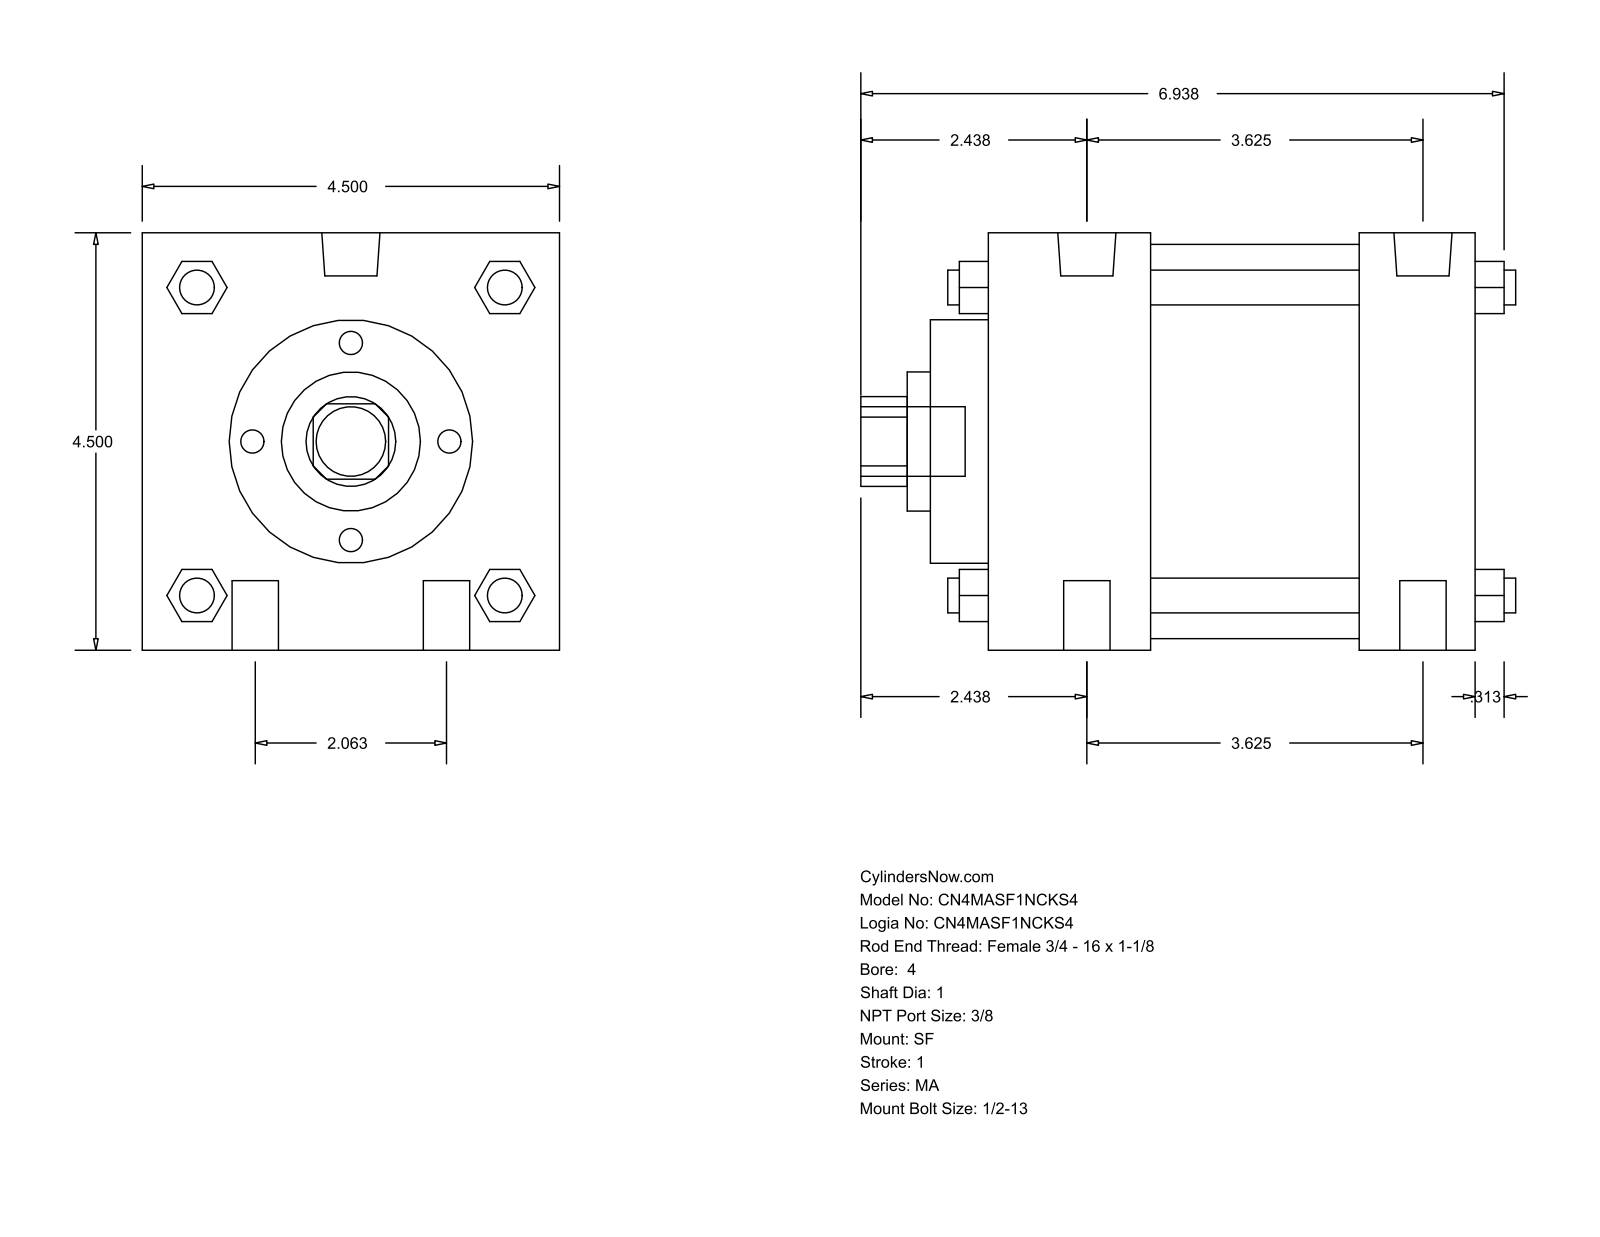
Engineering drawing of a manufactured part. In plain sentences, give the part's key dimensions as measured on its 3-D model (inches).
The part is named "MA_SF__0400_1". Its 3-D file was written by "GSSL Pune (CONFIG_CONTROL_DESIGN)". It is 0 solids with 126 faces: 95 planar, 31 cylindrical and 0 other. Overall it measures 7.063 by 4.5 by 4.5 inches. Round holes: 1 of diameter 1, 1 of diameter 1.5, 1 of diameter 2.625, 1 of diameter 4.25. Round bosses or shafts: 4 of diameter 0.5, 4 of diameter 0.375, 2 of diameter 0.627, 2 of diameter 0.437, 1 of diameter 0.75. Partial cylindrical surfaces (rounded edges, fillets, slot ends): 1 of radius 0.484. The main face-to-face distances are 4.5, 5.25, 4, 1.25, 1.75, 2.25, 3.5, 0.625, 2.375, 4.625.
